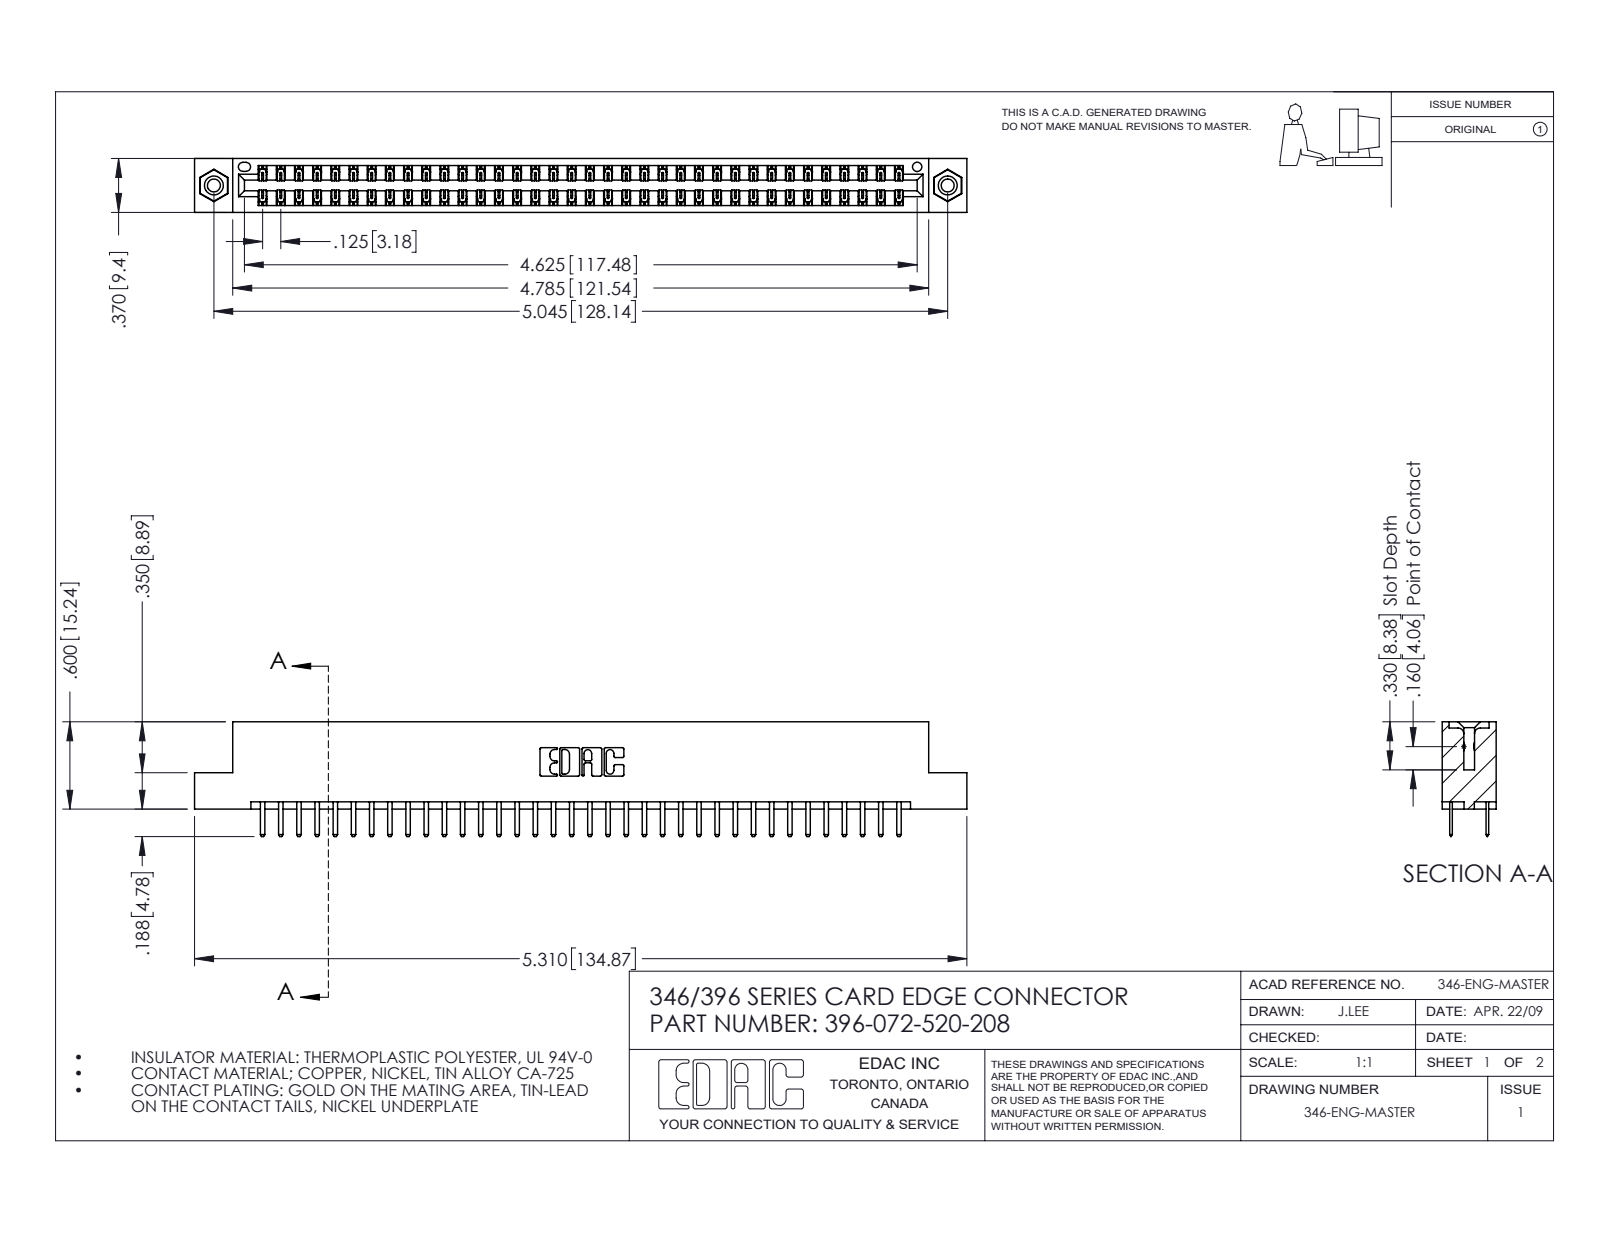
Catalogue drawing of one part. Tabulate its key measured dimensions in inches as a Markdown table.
| quantity | value |
| --- | --- |
| part name | 396-072-520-208; 345-292-001_345-293-120; 346 Part_Flush Mounting Lugs - 0.156 Dia-TI; 345-250-001_345-250-003-102 |
| STEP written by | SolidWorks 2016 (CONFIG_CONTROL_DESIGN) |
| units | inches |
| bodies | 75 solids, 4214 faces (2772 planar, 1426 cylindrical, 16 other) |
| overall size | 5.31 × 0.788 × 0.37 |
| volume | 0.797 in³ |
| surface area | 27.61 in² |
| round holes (diameter × count) | 0.089 × 2, 0.125 × 2, 0.156 × 2, 0.064 × 1 |
| round bosses / shafts (diameter × count) | 0.155 × 2 |
| partial cylindrical surfaces (radius × count) | 0.006 × 108, 0.01 × 76, 0.01 × 22, 0.007 × 6, 0.031 × 6, 0.026 × 3, 0.014 × 2, 0.022 × 2 |
| main face-to-face distances | 0.048, 0.322, 0.25, 0.37, 0.275, 0.072, 0.298, 0.025, 0.148, 0.222 |
| hole center spacings | 0.246, 4.836, 5.045 |
